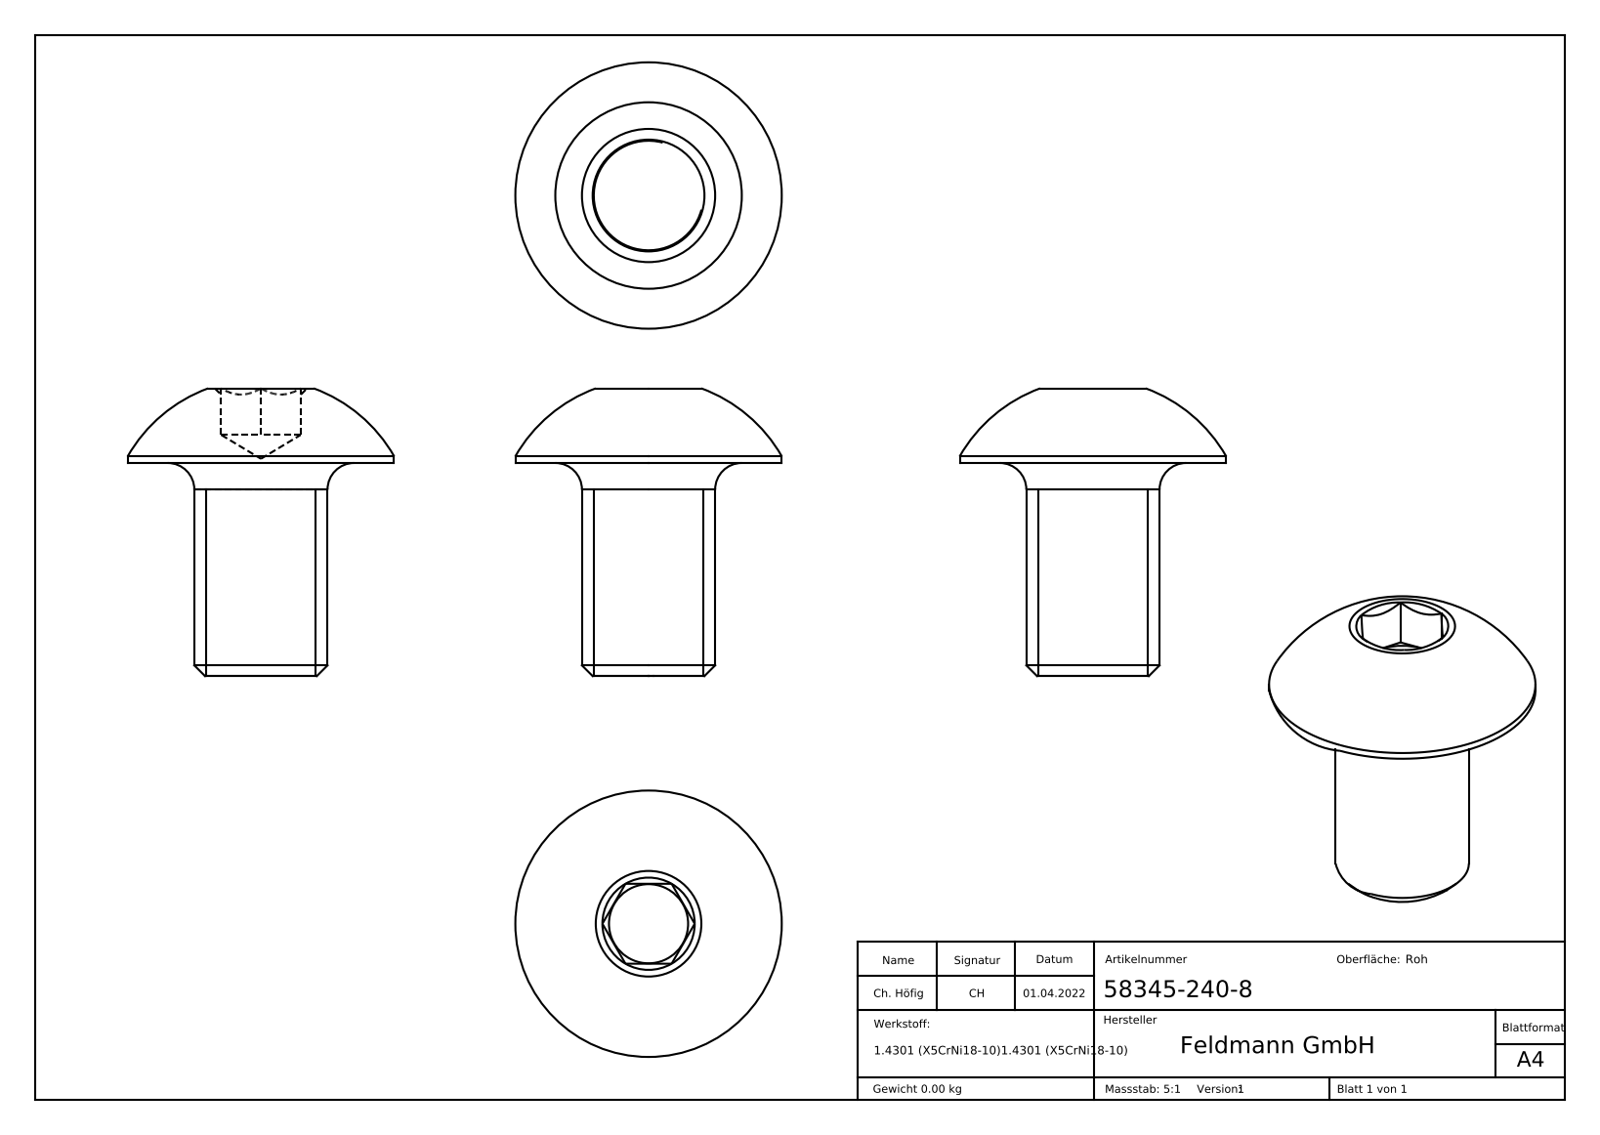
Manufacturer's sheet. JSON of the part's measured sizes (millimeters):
{"part_name": "58345-240-8", "step_written_by": "SolidWorks 2018 (CONFIG_CONTROL_DESIGN)", "units": "millimeters", "bodies": {"solids": 1, "faces": 287, "planar": 148, "cylindrical": 2, "other": 137}, "overall_size": [10.8, 10, 10], "volume_mm3": 288, "surface_area_mm2": 326, "round_bosses_or_shafts": [[10, 1], [5, 1]], "face_to_face_distances": [8, 3, 2.8, 10.8, 1.75, 1.05, 9.05, 3.1, 0.83, 0.34]}
